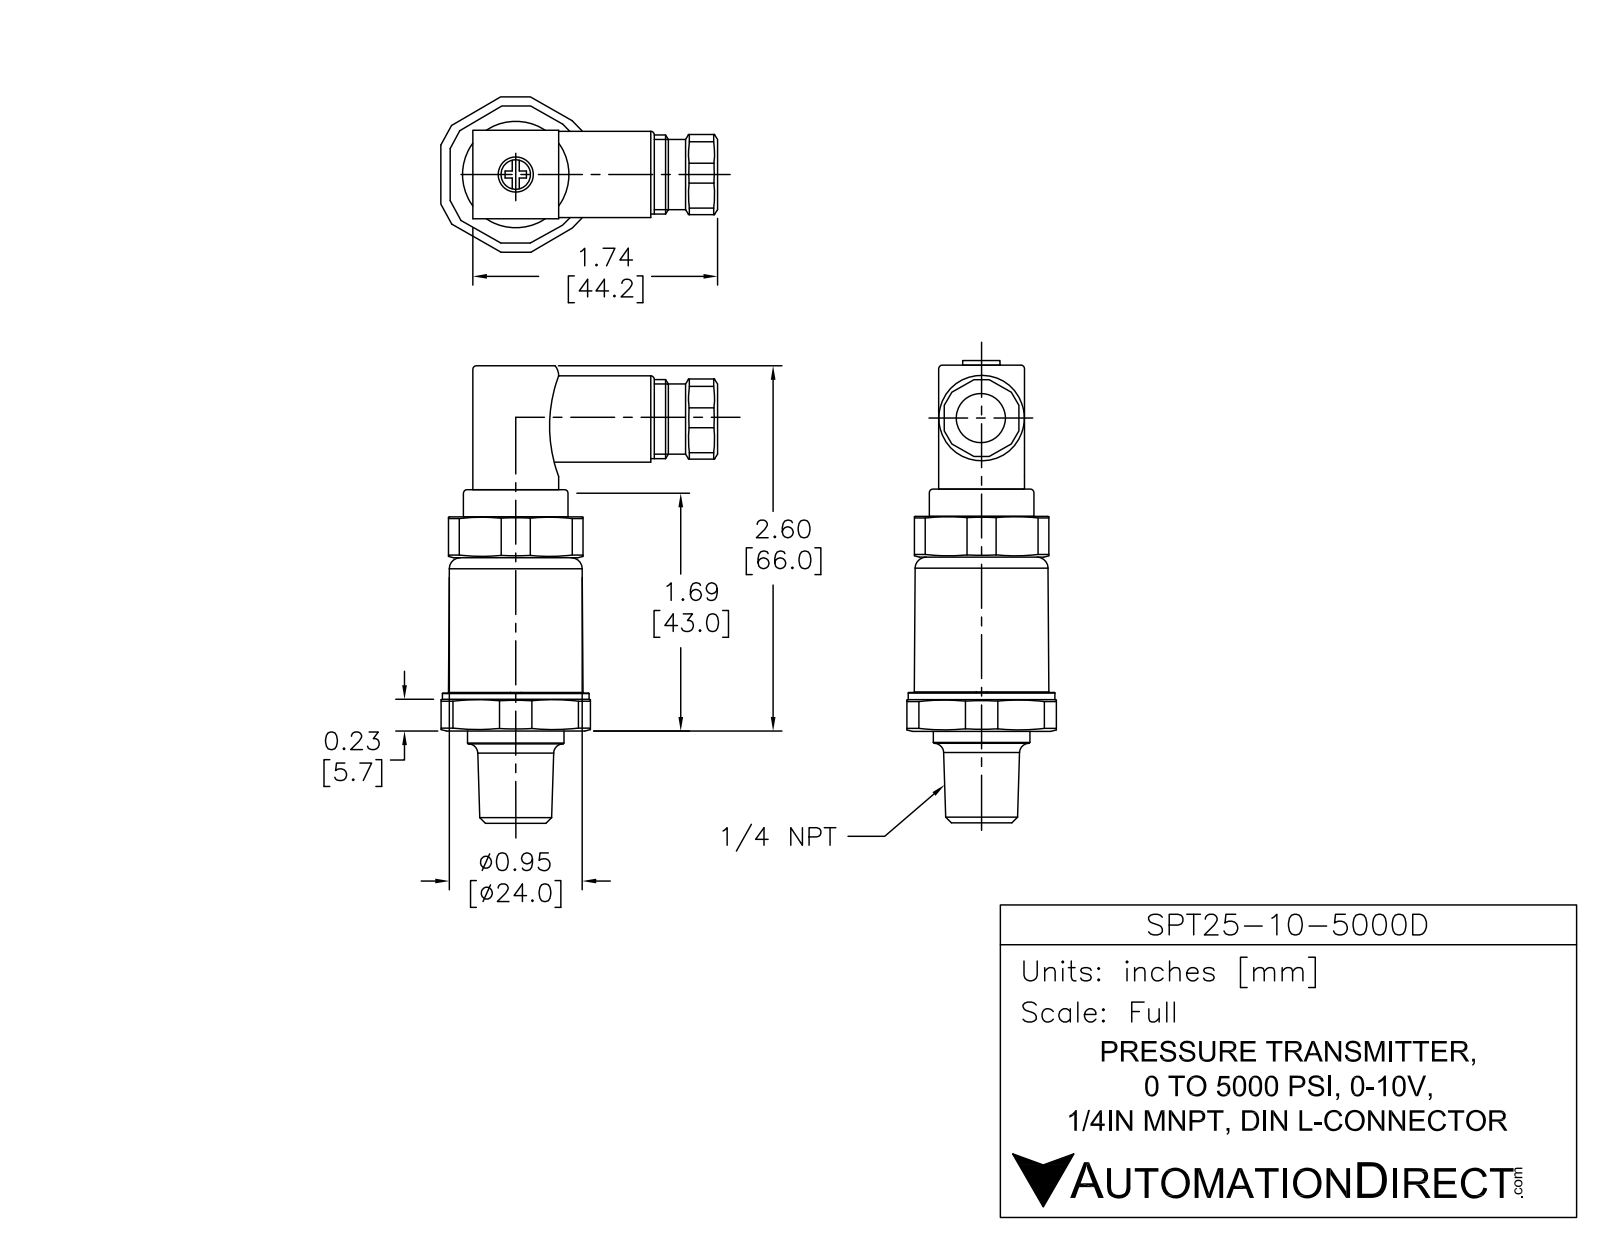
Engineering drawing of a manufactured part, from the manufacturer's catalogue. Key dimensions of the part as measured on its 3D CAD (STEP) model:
Part name (STEP PRODUCT): SPT25-10-5000D
STEP written by: SolidWorks 2011 (AUTOMOTIVE_DESIGN)
Units: millimetres
Bodies: 5 solids, 170 faces (96 planar, 64 cylindrical, 10 other)
Overall size (bounding box): 81.25 × 38.01 × 35.71
Volume: 27 900 mm³ · Surface area: 10 134 mm²
Round holes (diameter × count): ⌀1 ×1, ⌀3.3 ×1, ⌀7 ×1, ⌀8 ×1
Round bosses / shafts (diameter × count): ⌀26.75 ×1, ⌀24 ×1, ⌀17.5 ×1, ⌀15 ×1, ⌀14 ×1, ⌀11 ×1
Partial cylindrical surfaces — rounded edges, fillets, slot ends (radius × count): R1.5 ×8, R1.15 ×4, R2.25 ×4, R2 ×3, R1.15 ×1, R1.17 ×1, R14.5 ×1
Main face-to-face distances: 1.5, 29.5, 31, 15.75, 0.35, 15.4, 6.75, 37.75, 36.25, 5
Hole centre spacings: 1.33
